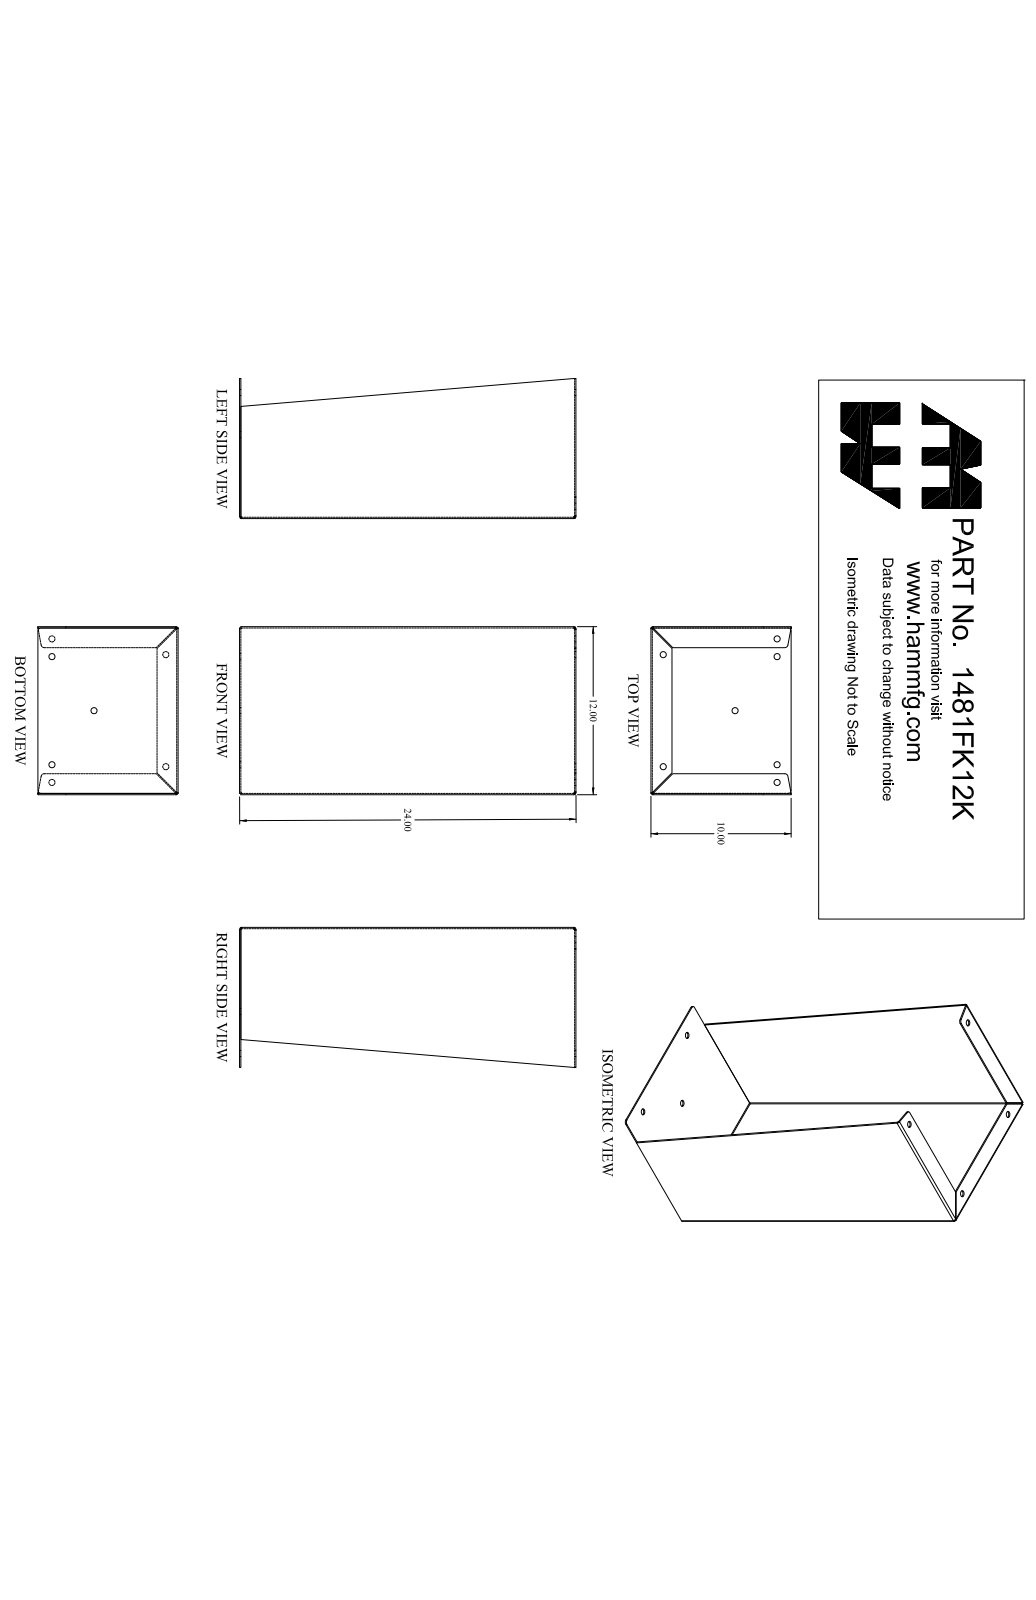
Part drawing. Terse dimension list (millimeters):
name: 1481FK12K_Default
written by: SolidWorks 2019 (CONFIG_CONTROL_DESIGN)
unit: mm
bodies: 1 solid, 78 faces (42 planar, 30 cylindrical, 6 other)
size: 609.6 × 304.8 × 254
volume: 1 348 000 mm³; area: 1 126 000 mm²
holes: 7× ⌀11.1
rounds: 6× R1.2, 6× R3.6, 4× R5.6
face distances: 2.4, 302.4, 300, 304.8, 2.4, 604.8, 607.2, 607.2, 609.6, 35.7
hole spacings: 124.2, 165.1, 206.4, 208.3, 287.1, 32.2, 32.2, 150.9
